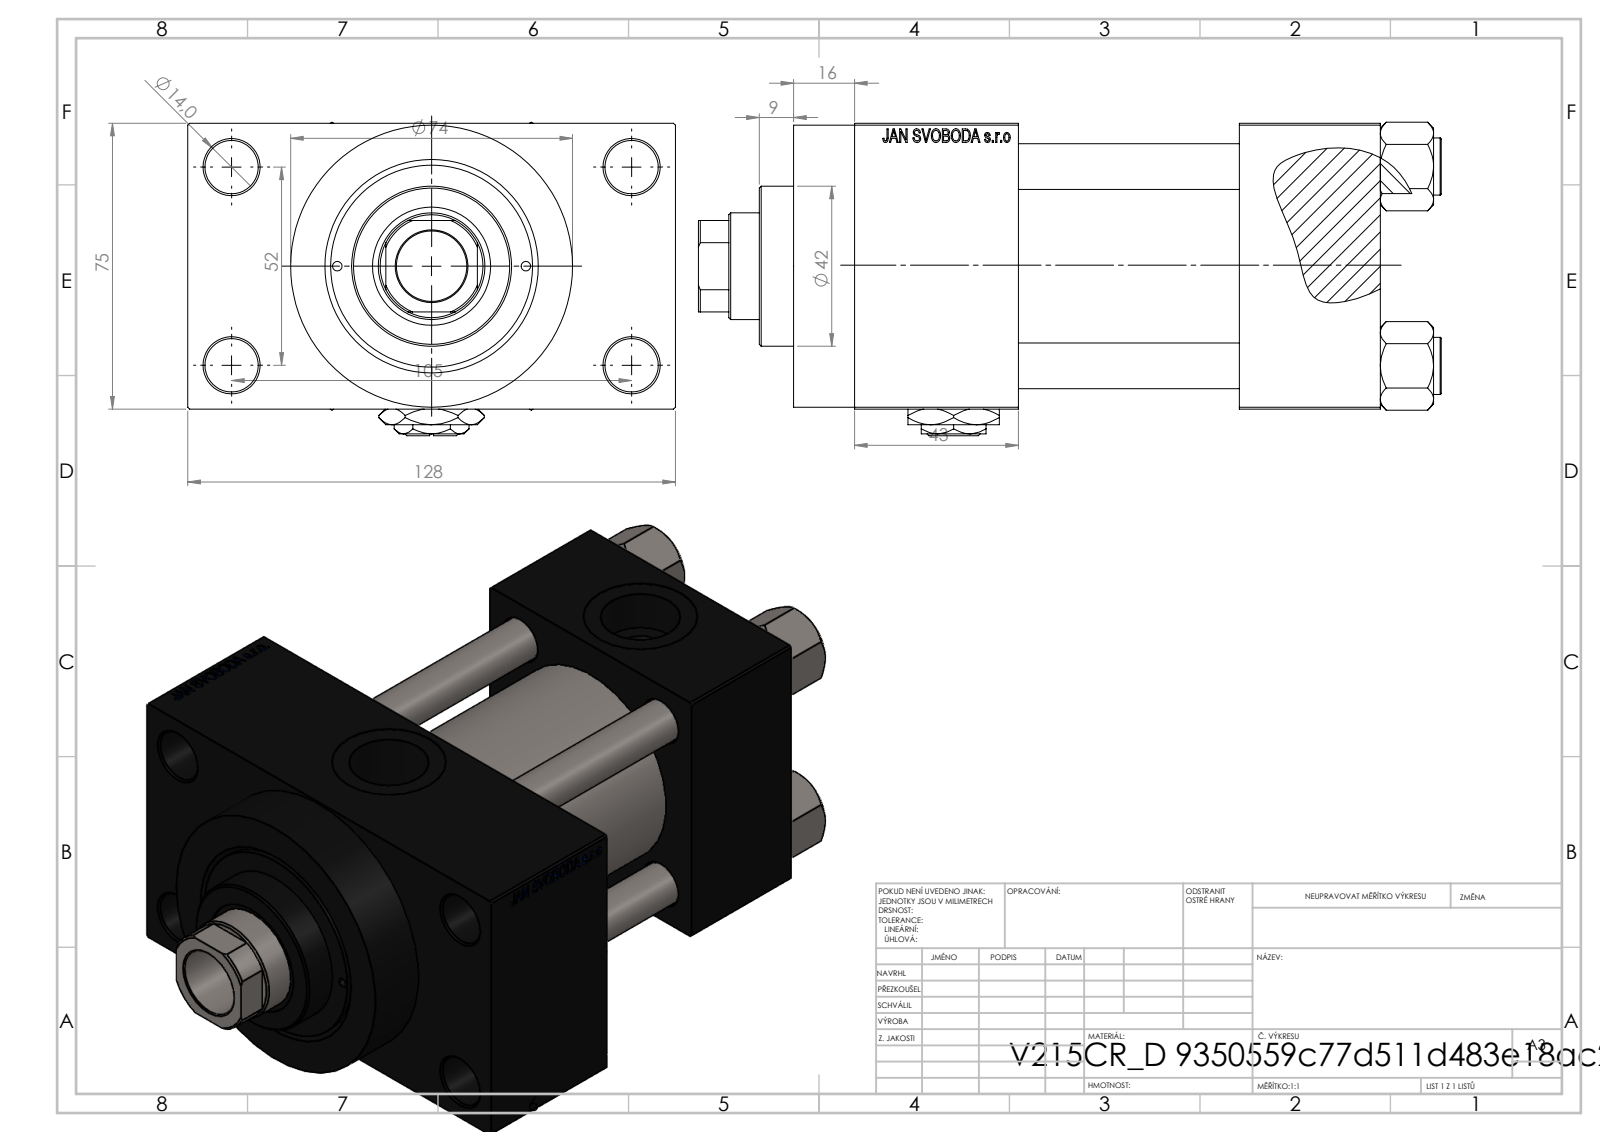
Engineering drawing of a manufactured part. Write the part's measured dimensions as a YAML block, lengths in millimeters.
part_name: "V215CR_VCP_D; V215CR_D_Body; V215CR_D_TYCINKA; NUT_M5_D (+2 more)"
step_written_by: "SolidWorks 2019 (CONFIG_CONTROL_DESIGN)"
units: millimeters
bodies: {solids: 12, faces: 1160, planar: 523, cylindrical: 97, other: 540}
overall_size: [195, 128, 82.27]
volume: 812777
surface_area: 170431
round_holes:
  - {diameter: 12, count: 4}
  - {diameter: 14, count: 4}
  - {diameter: 2.5, count: 2}
  - {diameter: 7, count: 2}
  - {diameter: 20.96, count: 2}
  - {diameter: 30, count: 2}
  - {diameter: 18.5, count: 1}
  - {diameter: 28, count: 1}
  - {diameter: 31, count: 1}
  - {diameter: 41, count: 1}
  - {diameter: 50, count: 1}
  - {diameter: 53, count: 1}
round_bosses_or_shafts:
  - {diameter: 15, count: 4}
  - {diameter: 74, count: 1}
  - {diameter: 56, count: 1}
  - {diameter: 42, count: 1}
partial_cylinders:
  - {radius: 13.5, count: 1}
face_to_face_distances: [75, 58, 37, 95, 26.5, 101.5, 138, 101, 43, 16]
hole_center_spacings: [26.19, 26.35, 36.98, 38.03, 52.3, 57.22, 58.43, 58.59]
